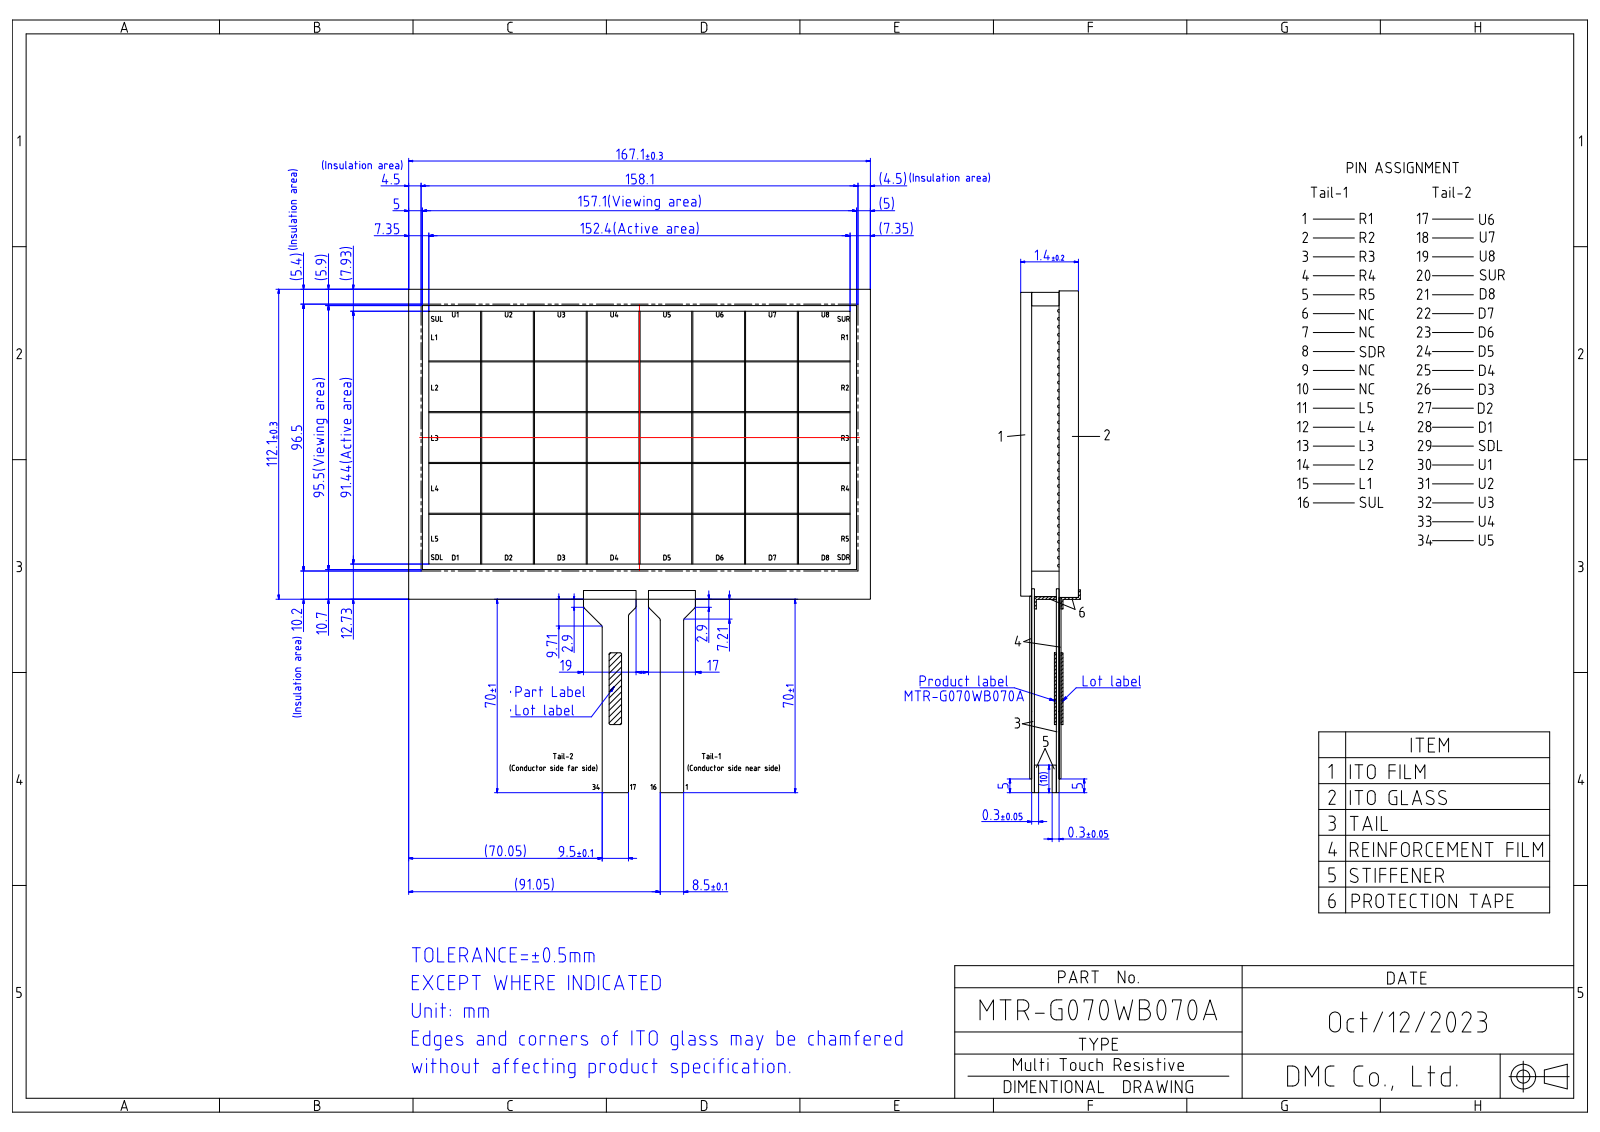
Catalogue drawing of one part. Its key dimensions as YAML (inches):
part_name: "MTR-G070WB070A"
step_written_by: "Autodesk Inventor 2020 (CONFIG_CONTROL_DESIGN)"
units: inches
bodies: {solids: 1, faces: 190, planar: 178, cylindrical: 12, other: 0}
overall_size: [9.21, 8.052, 0.059]
volume: 1.605
surface_area: 63.72
partial_cylinders:
  - {radius: 0.039, count: 8}
  - {radius: 0.008, count: 4}
face_to_face_distances: [0.055, 0.043, 0.047, 0.051, 4.413, 0.016, 6.579, 0.059, 0.02, 0.031]
